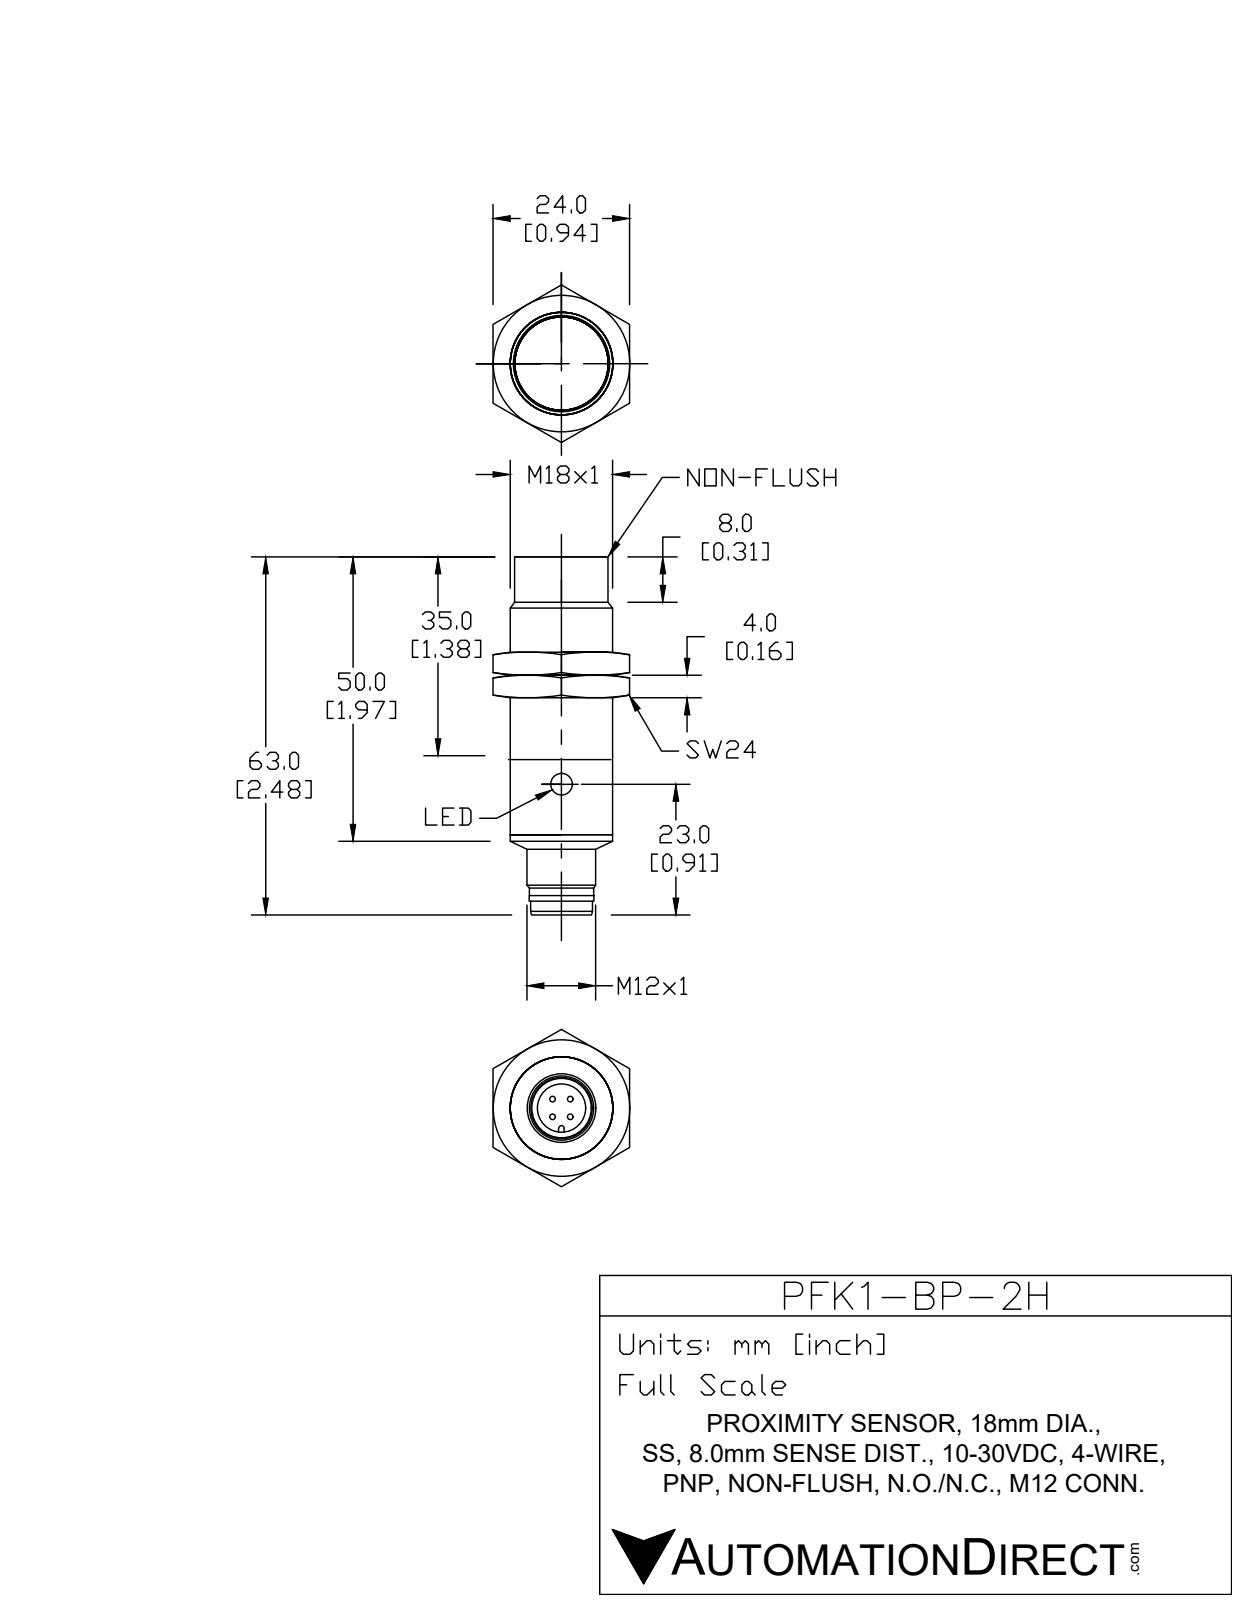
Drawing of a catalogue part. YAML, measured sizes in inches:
part_name: "PFK1-BP-2H"
step_written_by: "SolidWorks 2017 (AUTOMOTIVE_DESIGN)"
units: inches
bodies: {solids: 4, faces: 69, planar: 12, cylindrical: 35, other: 22}
overall_size: [2.484, 0.709, 0.709]
volume: 0.811
surface_area: 8.999
round_holes:
  - {diameter: 0.157, count: 1}
  - {diameter: 0.331, count: 1}
  - {diameter: 0.335, count: 1}
  - {diameter: 0.374, count: 1}
  - {diameter: 0.622, count: 1}
round_bosses_or_shafts:
  - {diameter: 0.039, count: 4}
  - {diameter: 0.709, count: 1}
  - {diameter: 0.472, count: 1}
  - {diameter: 0.413, count: 1}
  - {diameter: 0.37, count: 1}
partial_cylinders:
  - {radius: 0.024, count: 1}
  - {radius: 0.326, count: 1}
face_to_face_distances: [1.539, 0.394, 1.933, 2.087, 1.693, 0.154, 2.134, 1.74, 0.201, 0.047]
